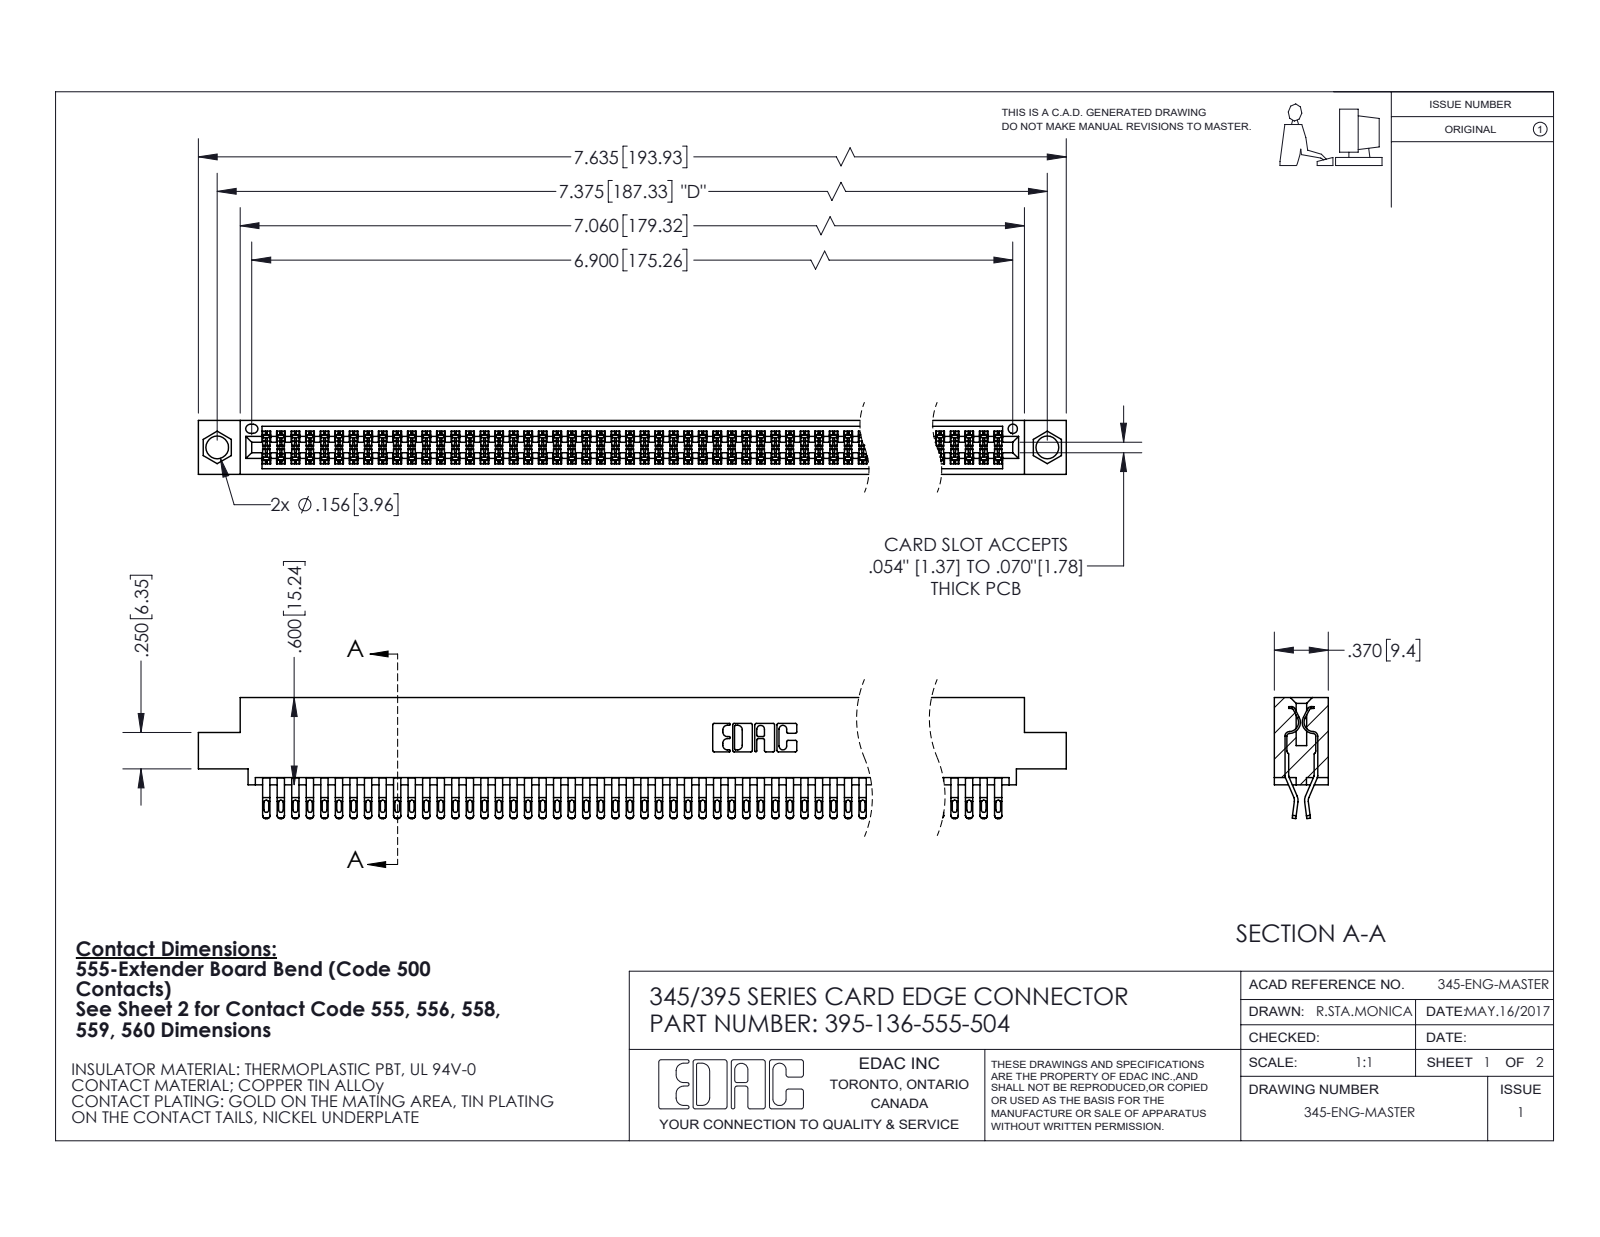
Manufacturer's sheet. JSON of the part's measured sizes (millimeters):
{"part_name": "395-136-555-504; 345 Part_0.110 Offset - 0.156 Dia-TI; 345-292-001_555 Tail", "step_written_by": "SolidWorks 2020 (CONFIG_CONTROL_DESIGN)", "units": "millimeters", "bodies": {"solids": 137, "faces": 7760, "planar": 4314, "cylindrical": 3446, "other": 0}, "overall_size": [193.9, 21.1, 9.4], "volume_mm3": 19290, "surface_area_mm2": 30340, "round_holes": [[4, 2], [1.6, 1]], "partial_cylinders_radius": [[0.4, 340], [0.2, 272], [0.5, 272], [0.3, 22], [0.2, 6], [0.8, 6], [0.7, 3], [0.3, 2]], "face_to_face_distances": [7.6, 1.8, 0.6, 9.4, 5.1, 2.5, 6.9, 5.7, 4.4, 3.8], "hole_center_spacings": [6.9, 181.3, 187.3]}
